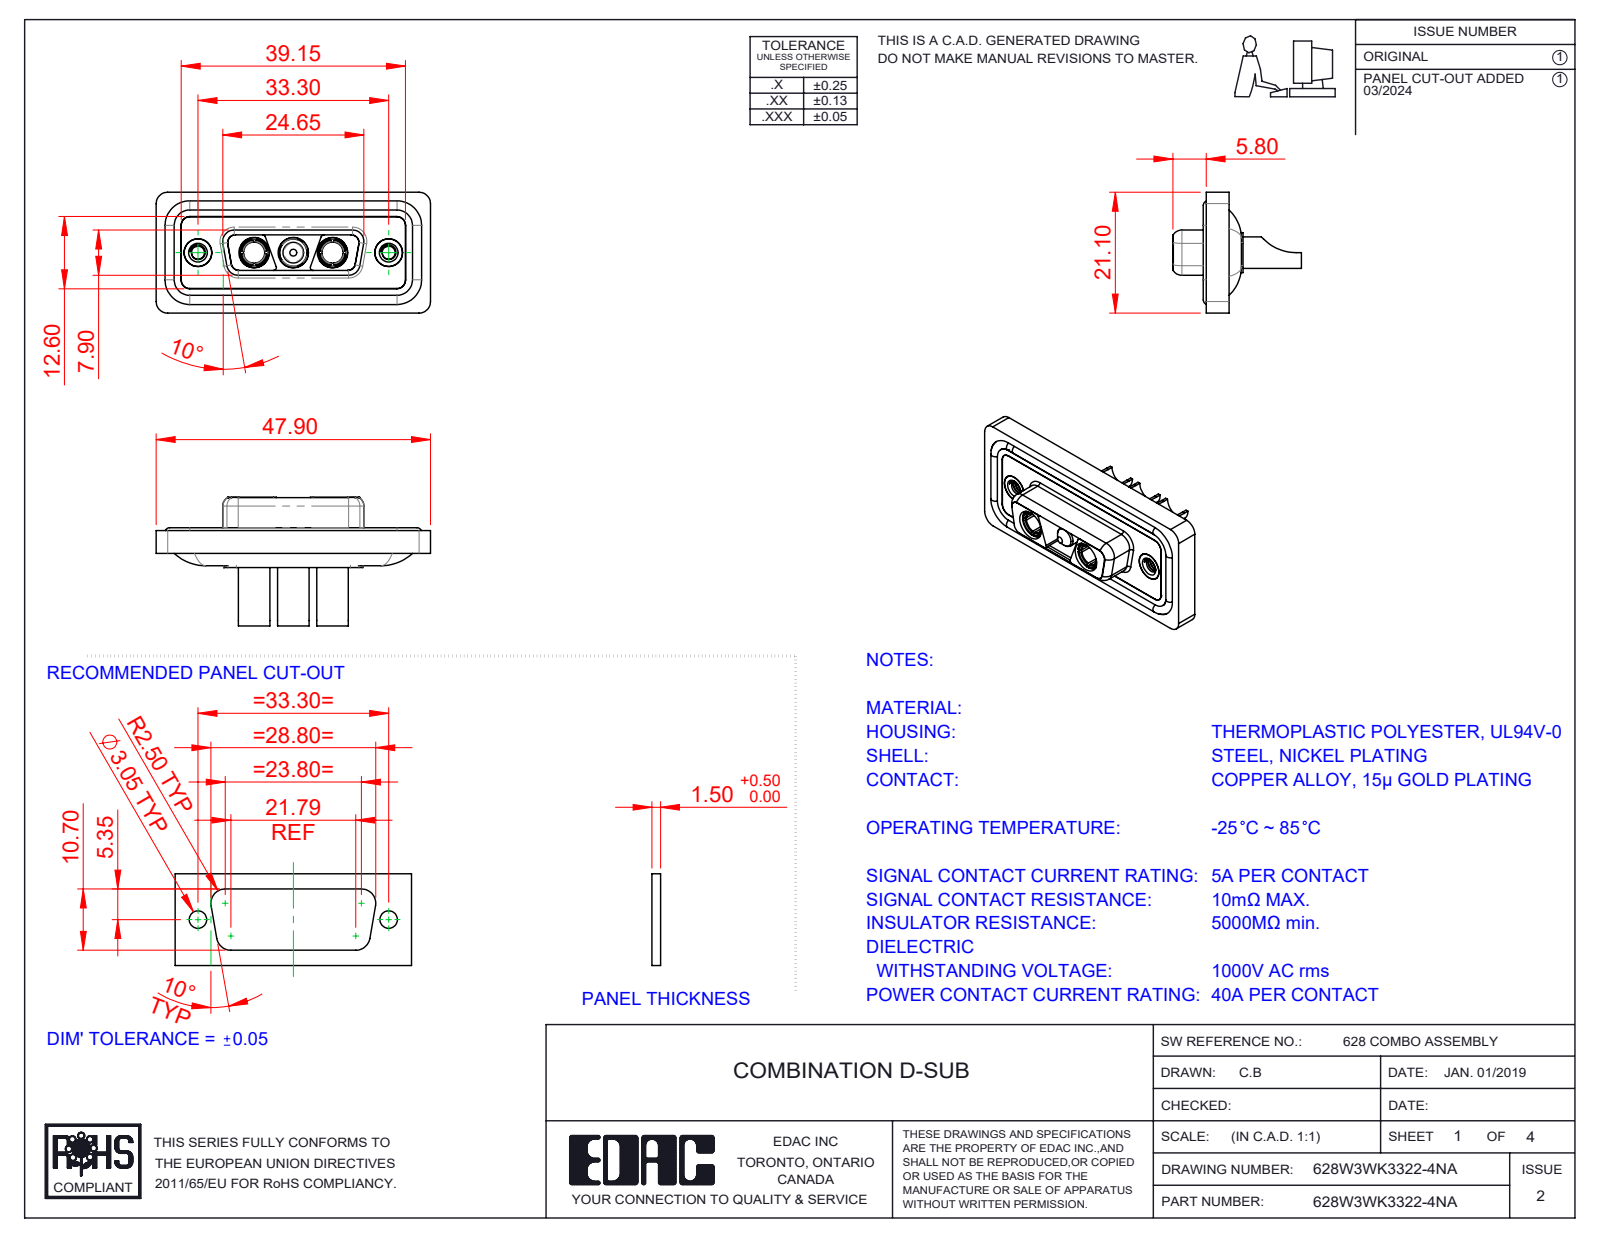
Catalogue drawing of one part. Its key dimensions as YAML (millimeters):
part_name: "628Combo Housing_3WK3; Power Socket_40A SC; 628Combo Shell Rear_15 Contacts; 628Combo Shell Front_15 Contacts (+4 more)"
step_written_by: "SolidWorks 2023 (CONFIG_CONTROL_DESIGN)"
units: millimeters
bodies: {solids: 13, faces: 591, planar: 184, cylindrical: 263, other: 144}
overall_size: [47.9, 22.45, 21.1]
volume: 5999
surface_area: 9922
round_holes:
  - {diameter: 4.85, count: 5}
  - {diameter: 4.6, count: 3}
  - {diameter: 5.3, count: 3}
  - {diameter: 2.26, count: 2}
  - {diameter: 3.7, count: 2}
  - {diameter: 4, count: 2}
  - {diameter: 4.05, count: 2}
  - {diameter: 5, count: 2}
round_bosses_or_shafts:
  - {diameter: 1.6, count: 4}
  - {diameter: 5.5, count: 3}
  - {diameter: 5.2, count: 3}
  - {diameter: 4.75, count: 3}
  - {diameter: 3.75, count: 3}
  - {diameter: 4.96, count: 2}
  - {diameter: 4.95, count: 2}
  - {diameter: 4.8, count: 2}
partial_cylinders:
  - {radius: 1.5, count: 22}
  - {radius: 2, count: 20}
  - {radius: 1.35, count: 12}
  - {radius: 0.5, count: 8}
  - {radius: 1.6, count: 8}
  - {radius: 0.25, count: 4}
  - {radius: 0.6, count: 4}
  - {radius: 0.65, count: 4}
face_to_face_distances: [0.4, 1.6, 0.5, 1.1, 2.9, 5.65, 1.8, 7.05, 5.35, 6.6]
hole_center_spacings: [6.85, 9.8, 16.65, 23.5, 13.7, 33.3]
